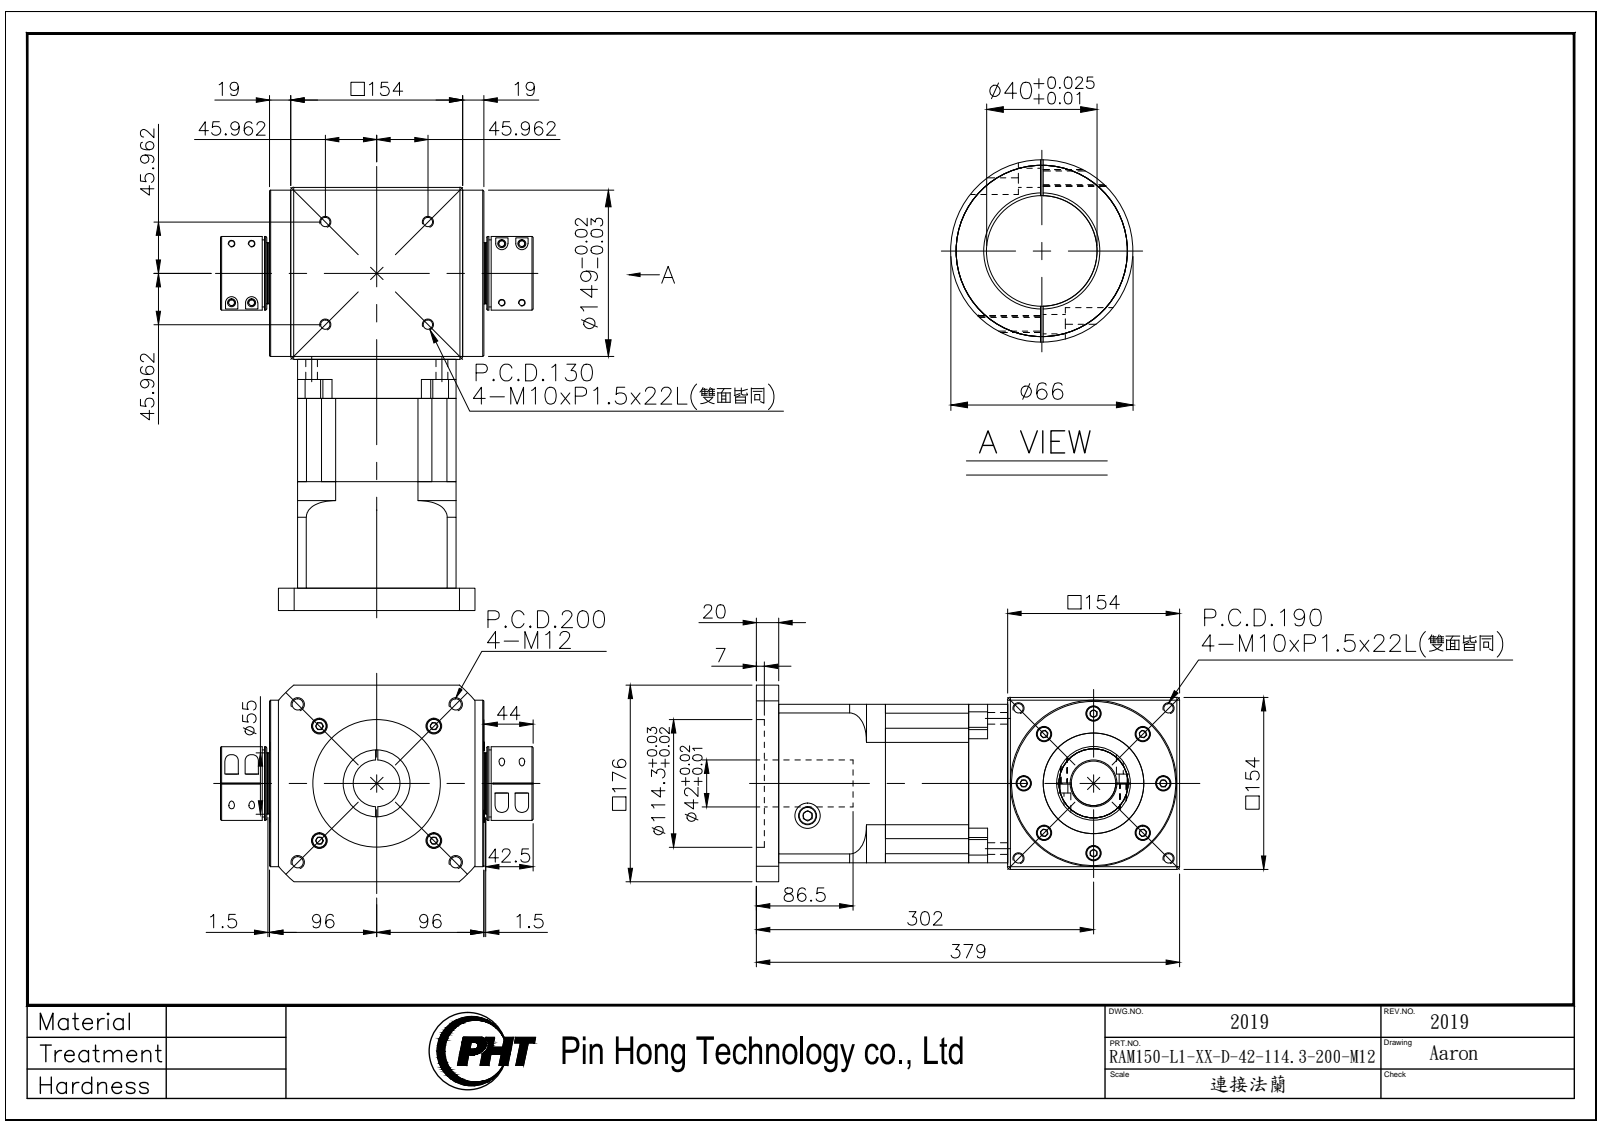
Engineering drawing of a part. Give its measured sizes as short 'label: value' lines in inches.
name: RAM150-L1-XX-D-42-114.3-200-M12_2019
written by: SolidWorks 2016 (AUTOMOTIVE_DESIGN)
unit: in
bodies: 4 solids, 1262 faces (612 planar, 432 cylindrical, 218 other)
size: 14.921 × 11.024 × 6.929
volume: 497.5 in³; area: 987.1 in²
holes: 12× ⌀0.335, 12× ⌀0.354, 12× ⌀0.551, 8× ⌀0.433, 8× ⌀0.689, 6× ⌀0.276, 4× ⌀0.268, 4× ⌀0.402, 4× ⌀0.413, 2× ⌀0.886, 1× ⌀1.575, 1× ⌀1.654
bosses: 12× ⌀0.63, 8× ⌀0.413, 8× ⌀0.394, 8× ⌀0.236, 4× ⌀0.512, 1× ⌀5.866, 1× ⌀5.118, 1× ⌀3.543
rounds: 8× R0.139, 8× R0.217, 4× R0.394, 1× R3.15, 1× R3.74, 1× R4.228, 1× R4.528
face distances: 0.236, 5.827, 6.063, 5.591, 2.933, 4.311, 1.378, 0.984, 10.374, 7.441
hole spacings: 2.795, 0.737, 0.74, 0.908, 1.433, 1.883, 2.651, 3.265
